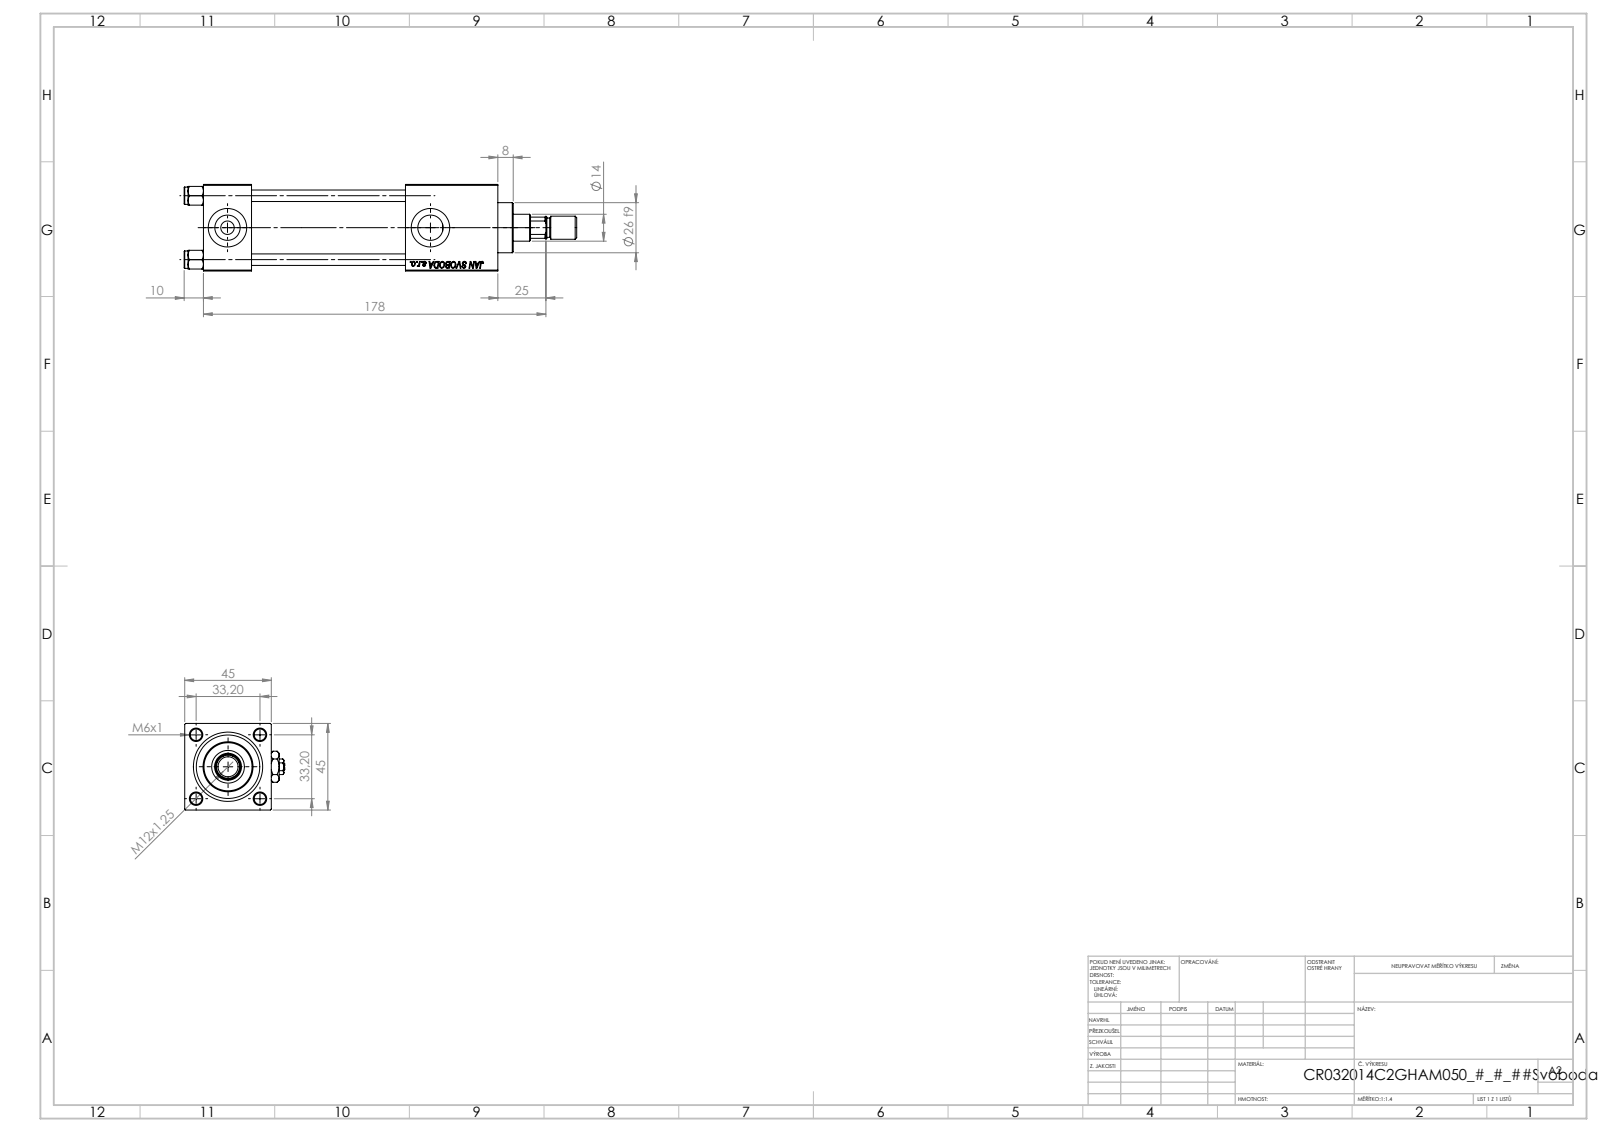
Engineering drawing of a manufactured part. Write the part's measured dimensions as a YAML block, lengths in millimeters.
part_name: "V215CR_VCP_C; ROD_END_AH; NUT_M5_C; V215_VC_A (+3 more)"
step_written_by: "SolidWorks 2019 (CONFIG_CONTROL_DESIGN)"
units: millimeters
bodies: {solids: 13, faces: 1214, planar: 552, cylindrical: 98, other: 564}
overall_size: [204, 52, 45]
volume: 212680
surface_area: 79192
round_holes:
  - {diameter: 6, count: 4}
  - {diameter: 7, count: 2}
  - {diameter: 13.16, count: 2}
  - {diameter: 20, count: 2}
  - {diameter: 6.5, count: 1}
  - {diameter: 14, count: 1}
  - {diameter: 17, count: 1}
  - {diameter: 24, count: 1}
  - {diameter: 32, count: 1}
  - {diameter: 33, count: 1}
round_bosses_or_shafts:
  - {diameter: 9, count: 4}
  - {diameter: 38, count: 1}
  - {diameter: 26, count: 1}
  - {diameter: 12, count: 1}
  - {diameter: 10, count: 1}
partial_cylinders:
  - {radius: 6.5, count: 1}
face_to_face_distances: [45, 25, 153, 128, 105, 80, 48, 124.3, 99.3, 19.3]
hole_center_spacings: [23.48, 33.2, 46.95, 105.5]
